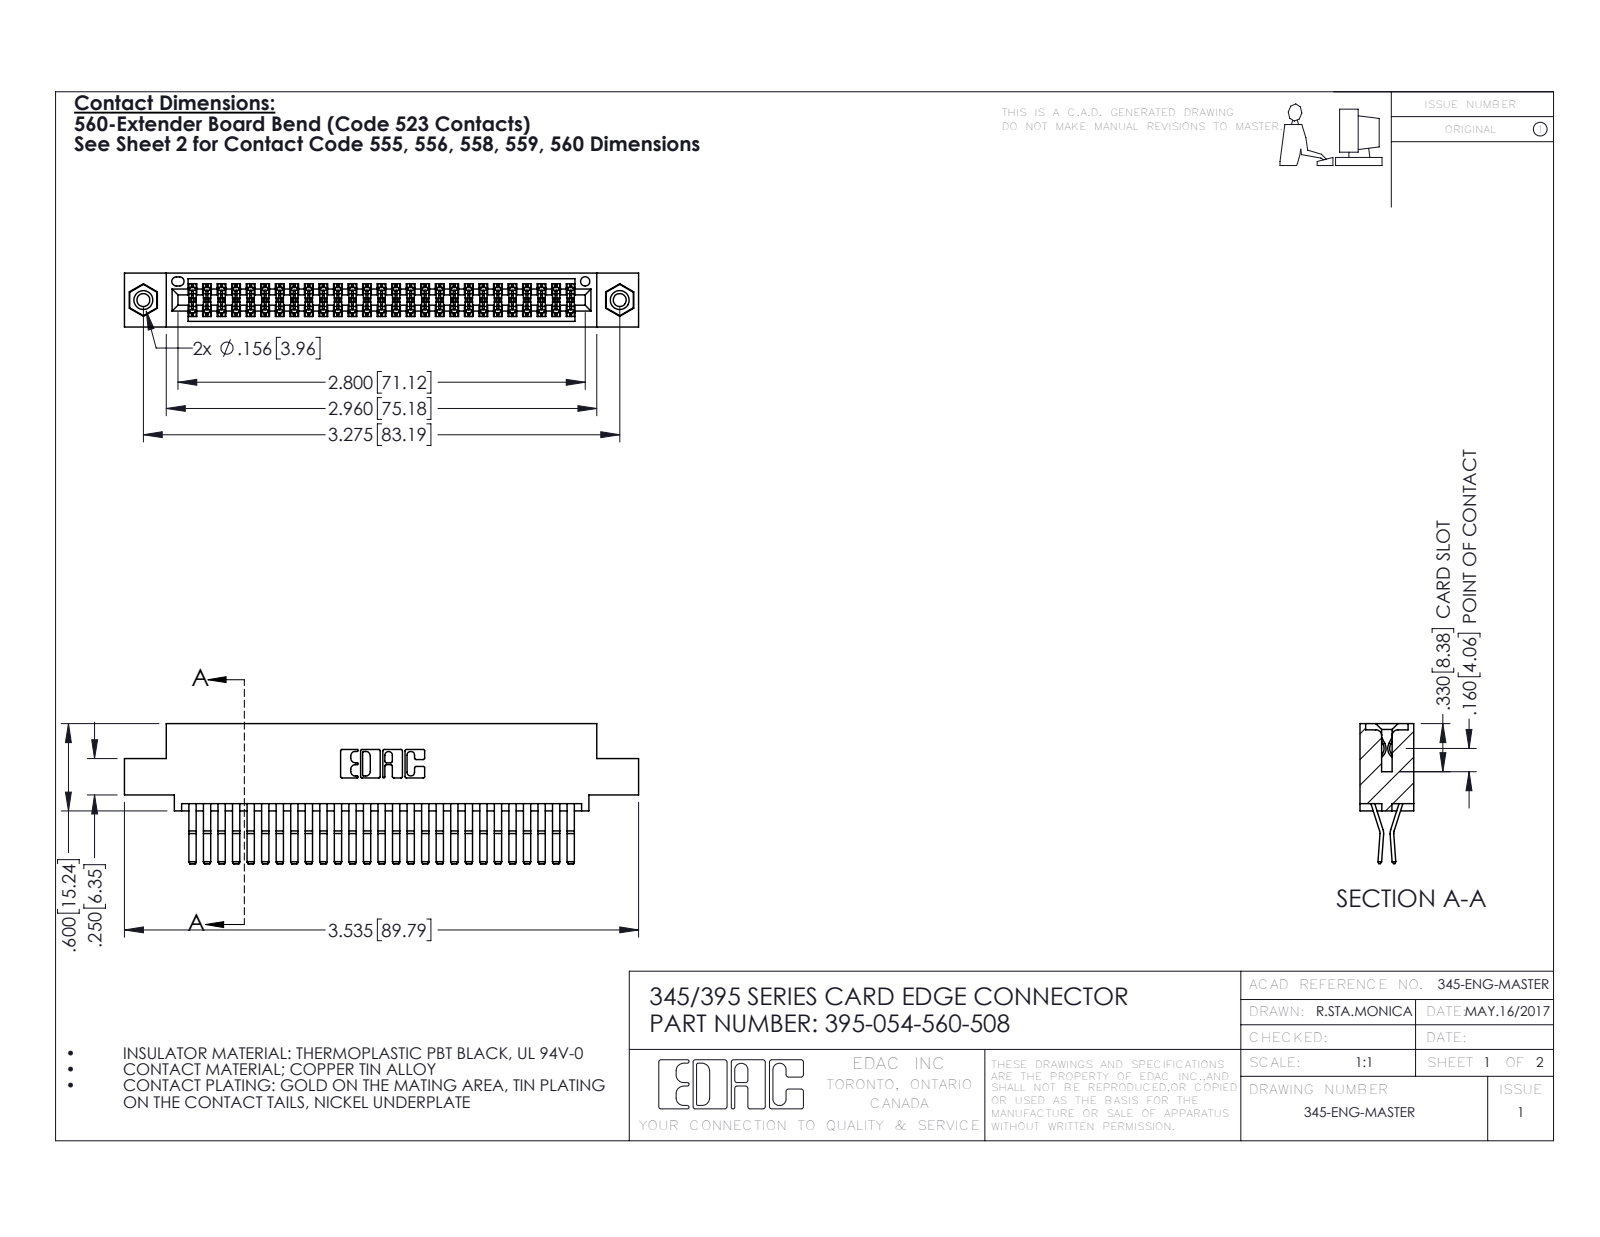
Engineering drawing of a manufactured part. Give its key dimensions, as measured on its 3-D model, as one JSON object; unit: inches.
{"part_name": "345-250-001_345-250-003-102; 345-292-001_560 Tail; 345 Part_0.110 Offset - 0.156 Dia-TI; 395-054-560-508", "step_written_by": "SolidWorks 2016 (CONFIG_CONTROL_DESIGN)", "units": "inches", "bodies": {"solids": 57, "faces": 2998, "planar": 1898, "cylindrical": 1084, "other": 16}, "overall_size": [3.535, 0.962, 0.37], "volume_in3": 0.54, "surface_area_in2": 21.42, "round_holes": [[0.089, 2], [0.125, 2], [0.156, 2], [0.064, 1]], "round_bosses_or_shafts": [[0.155, 2]], "partial_cylinders_radius": [[0.006, 81], [0.01, 22], [0.007, 6], [0.031, 6], [0.026, 3], [0.01, 2], [0.014, 2], [0.019, 2]], "face_to_face_distances": [0.025, 0.072, 0.298, 0.37, 0.2, 0.098, 0.272, 0.225, 0.175, 0.149], "hole_center_spacings": [0.27, 3.04, 3.275]}
